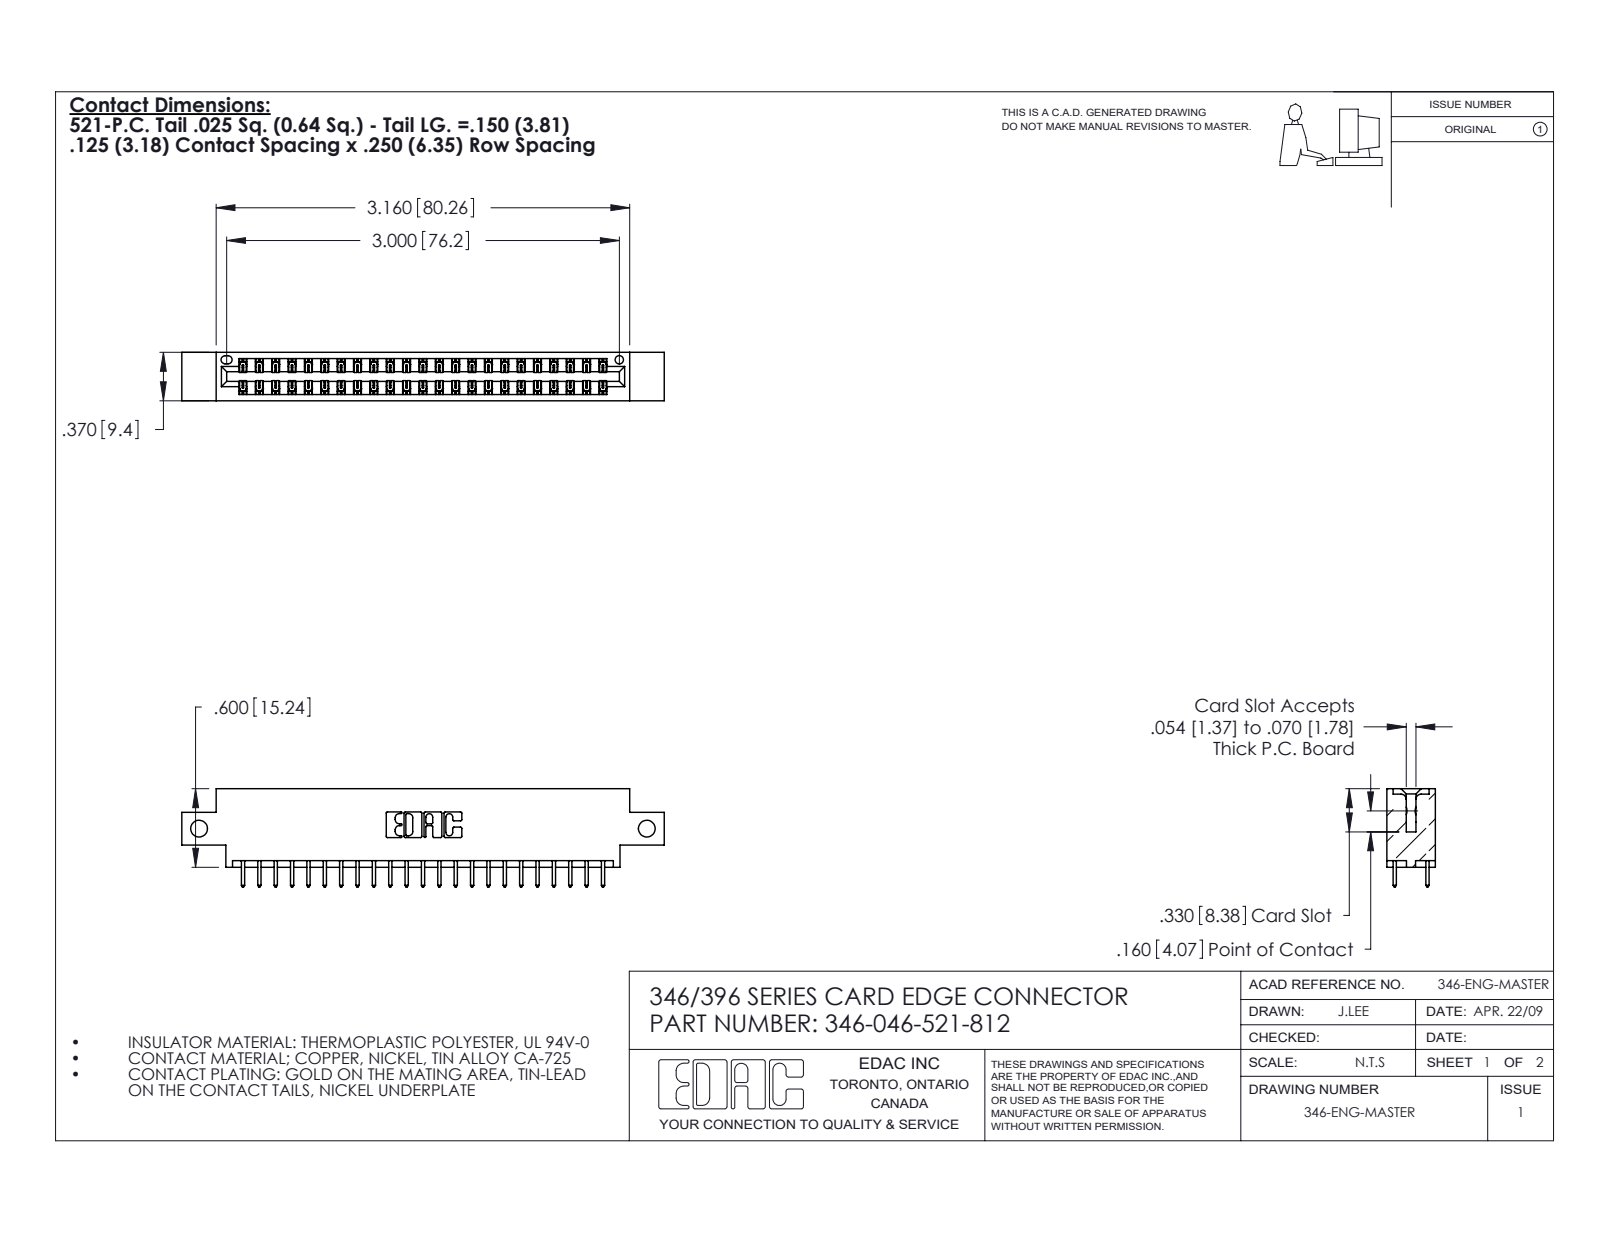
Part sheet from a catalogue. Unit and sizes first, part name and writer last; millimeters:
Units: millimetres
Overall size (bounding box): 93.6 × 19.1 × 9.4
Round holes (diameter × count): ⌀3.3 ×2, ⌀1.6 ×1
Partial cylindrical surfaces — rounded edges, fillets, slot ends (radius × count): R0.2 ×69, R0.3 ×46, R0.3 ×22, R0.2 ×6, R0.8 ×6, R0.7 ×3, R0.4 ×2, R0.6 ×2
Main face-to-face distances: 1.2, 8.2, 9.4, 6.4, 1.8, 7.6, 0.6, 7, 3.8, 5.6
Hole centre spacings: 86.9
Volume: 8 720 mm³ · Surface area: 11 600 mm²
Bodies: 47 solids, 2518 faces (1690 planar, 828 cylindrical, 0 other)
Part name (STEP PRODUCT): 346 Part_0.170 Offset - Side Mount; 346-046-521-812; 345-292-001_345-293-121
STEP written by: SolidWorks 2020 (CONFIG_CONTROL_DESIGN)
